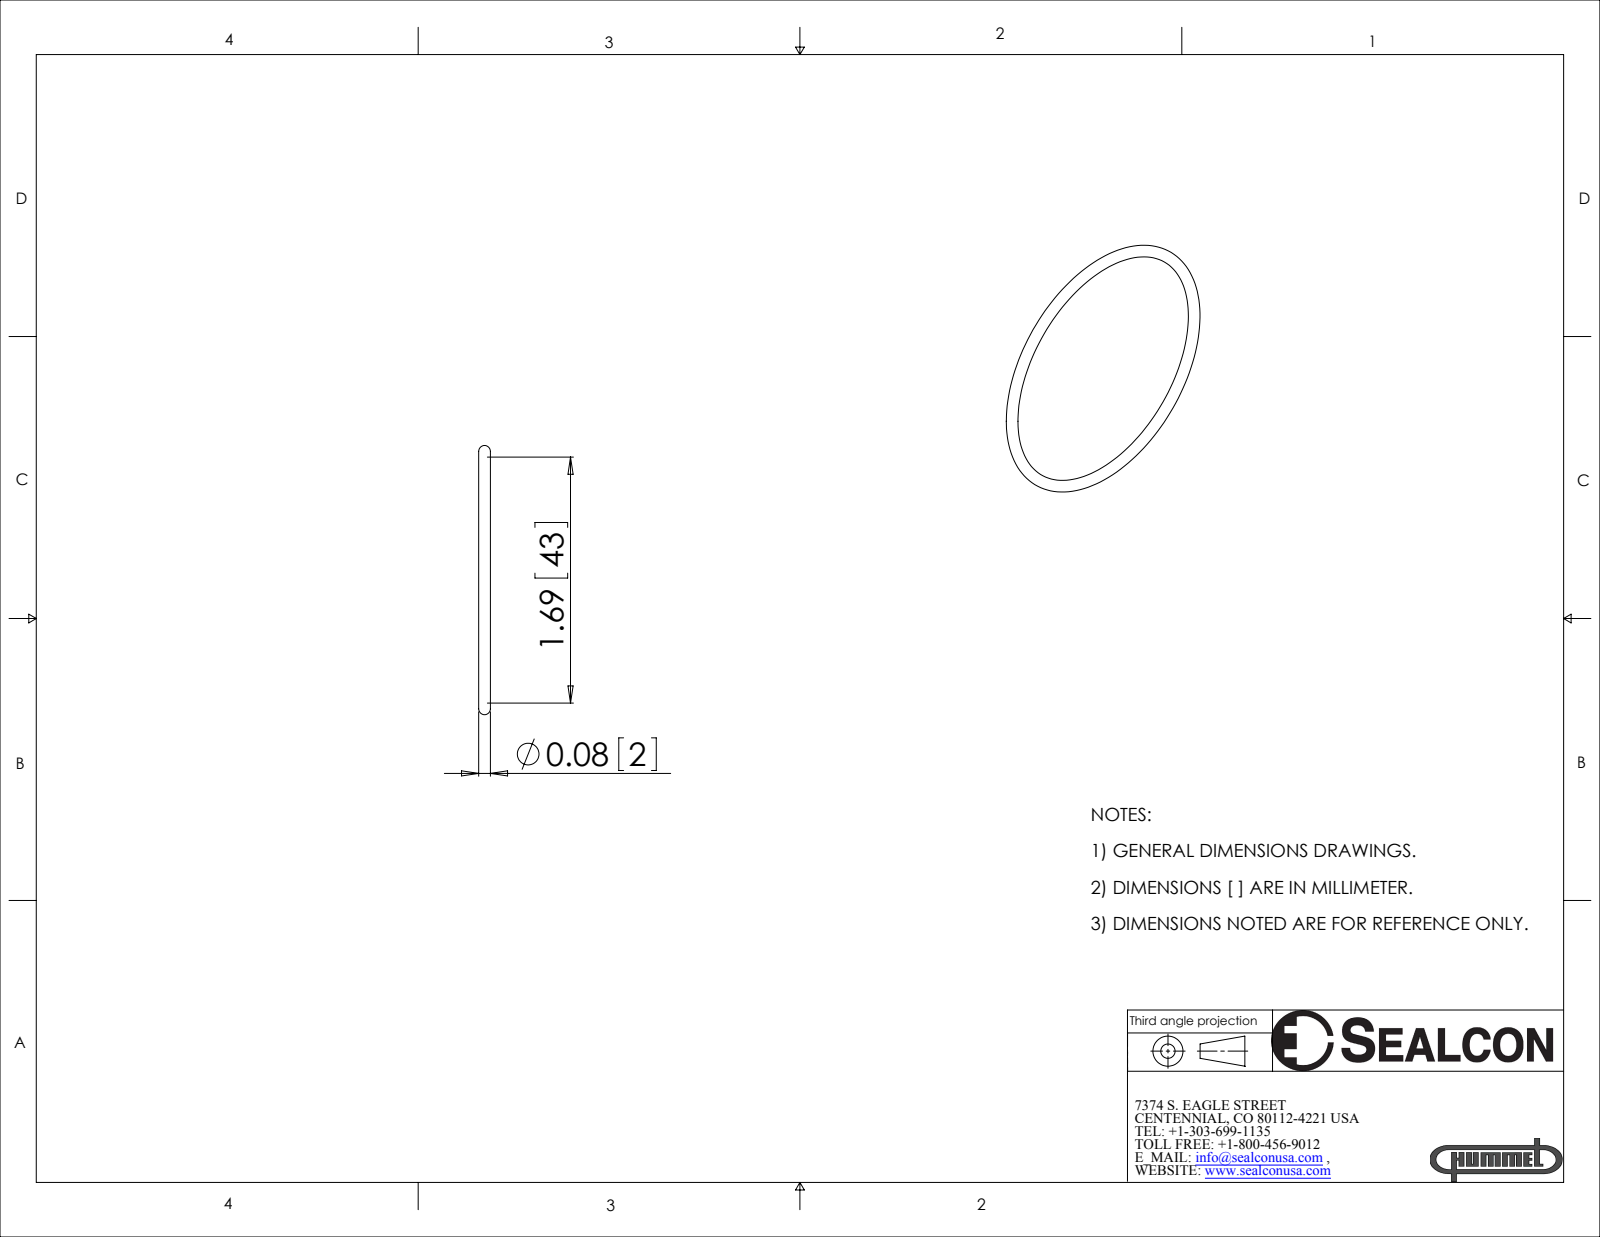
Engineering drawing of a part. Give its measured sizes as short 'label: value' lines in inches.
name: OM-50-SI
written by: SolidWorks 2008 (CONFIG_CONTROL_DESIGN)
unit: in
bodies: 1 solid, 4 faces (0 planar, 0 cylindrical, 4 other)
size: 1.85 × 1.85 × 0.08
volume: 0.028 in³; area: 1.398 in²
